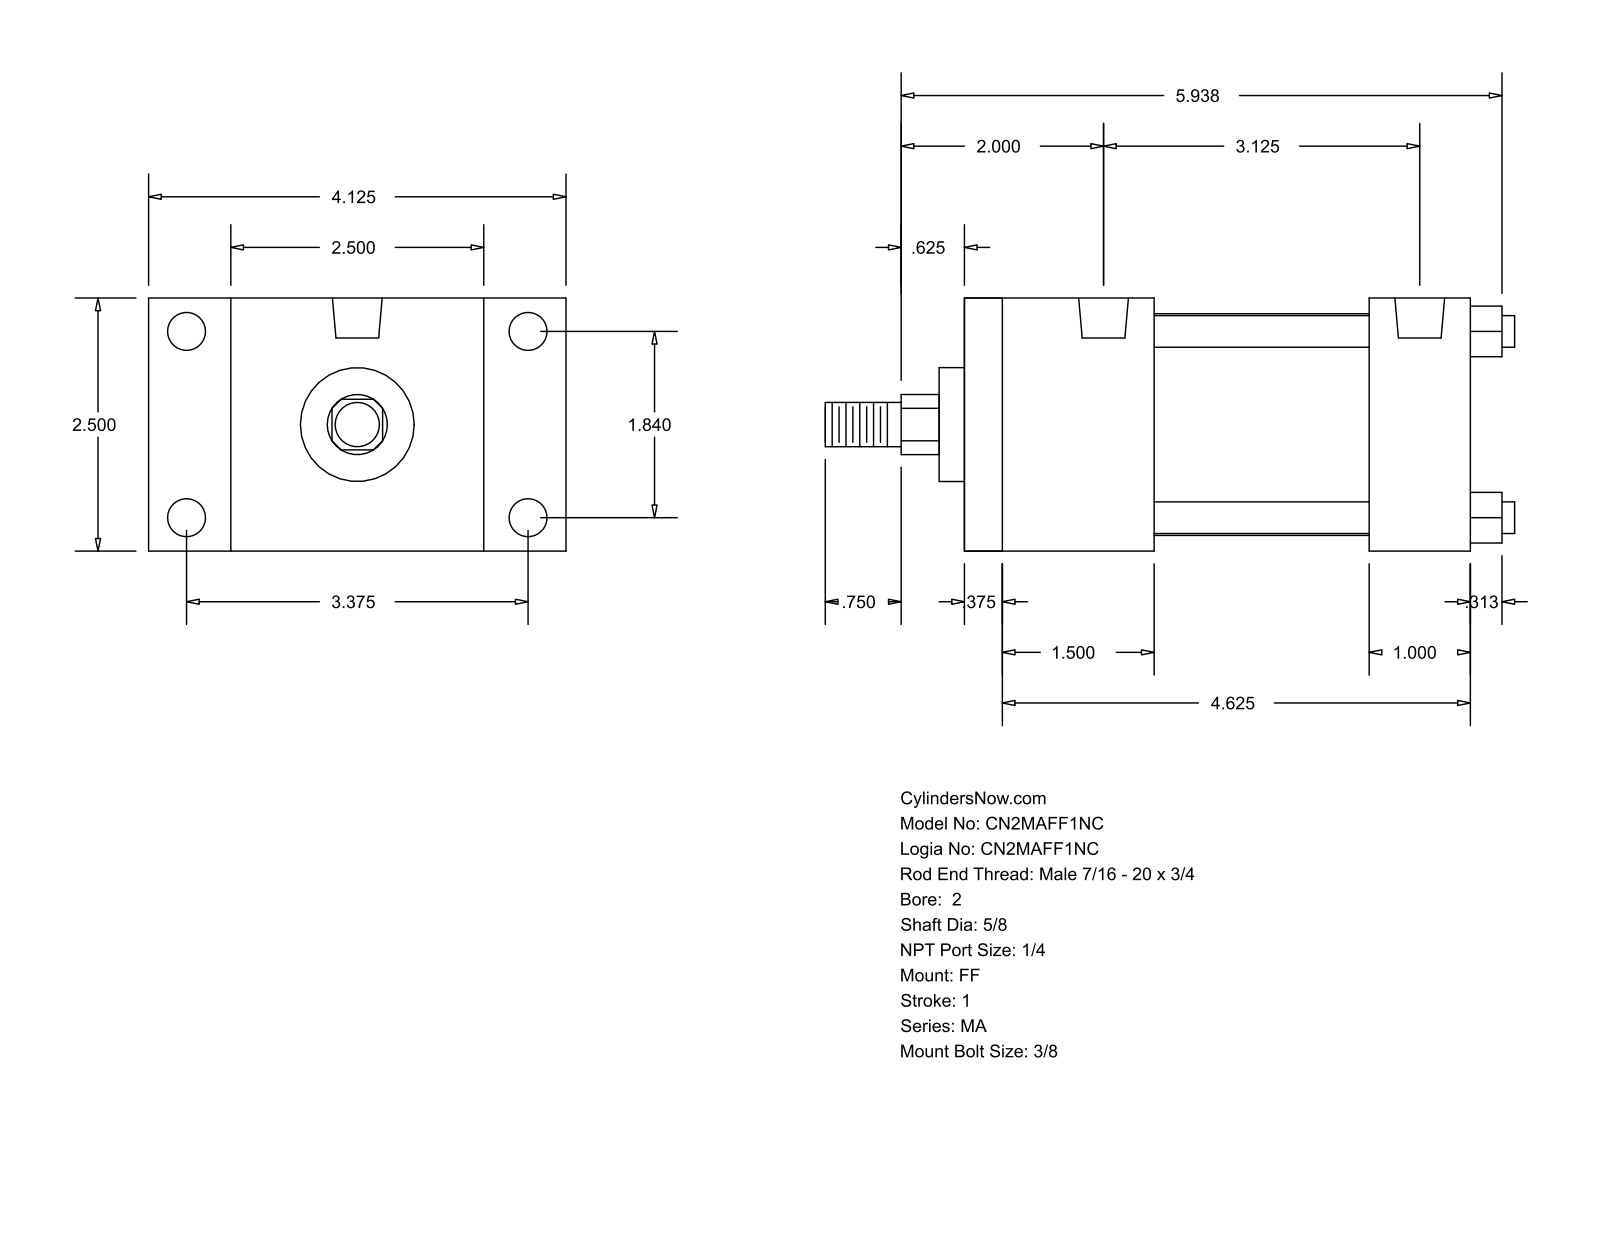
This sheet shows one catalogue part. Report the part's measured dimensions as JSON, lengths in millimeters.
{"part_name": "MA_FF__0200_0.625", "step_written_by": "GSSL Pune (CONFIG_CONTROL_DESIGN)", "units": "millimeters", "bodies": {"solids": 0, "faces": 92, "planar": 64, "cylindrical": 28, "other": 0}, "overall_size": [173.04, 104.78, 63.5], "round_holes": [[7.94, 4], [9.53, 4], [12.49, 2]], "round_bosses_or_shafts": [[7.94, 4], [55.63, 1], [28.57, 1], [15.88, 1], [11.11, 1]], "partial_cylinders_radius": [[7.54, 1]], "face_to_face_distances": [63.5, 127, 9.52, 117.48, 53.97, 38.1, 47.62, 101.59, 92.07, 79.38], "hole_center_spacings": [46.74, 79.38, 85.72, 97.63]}
